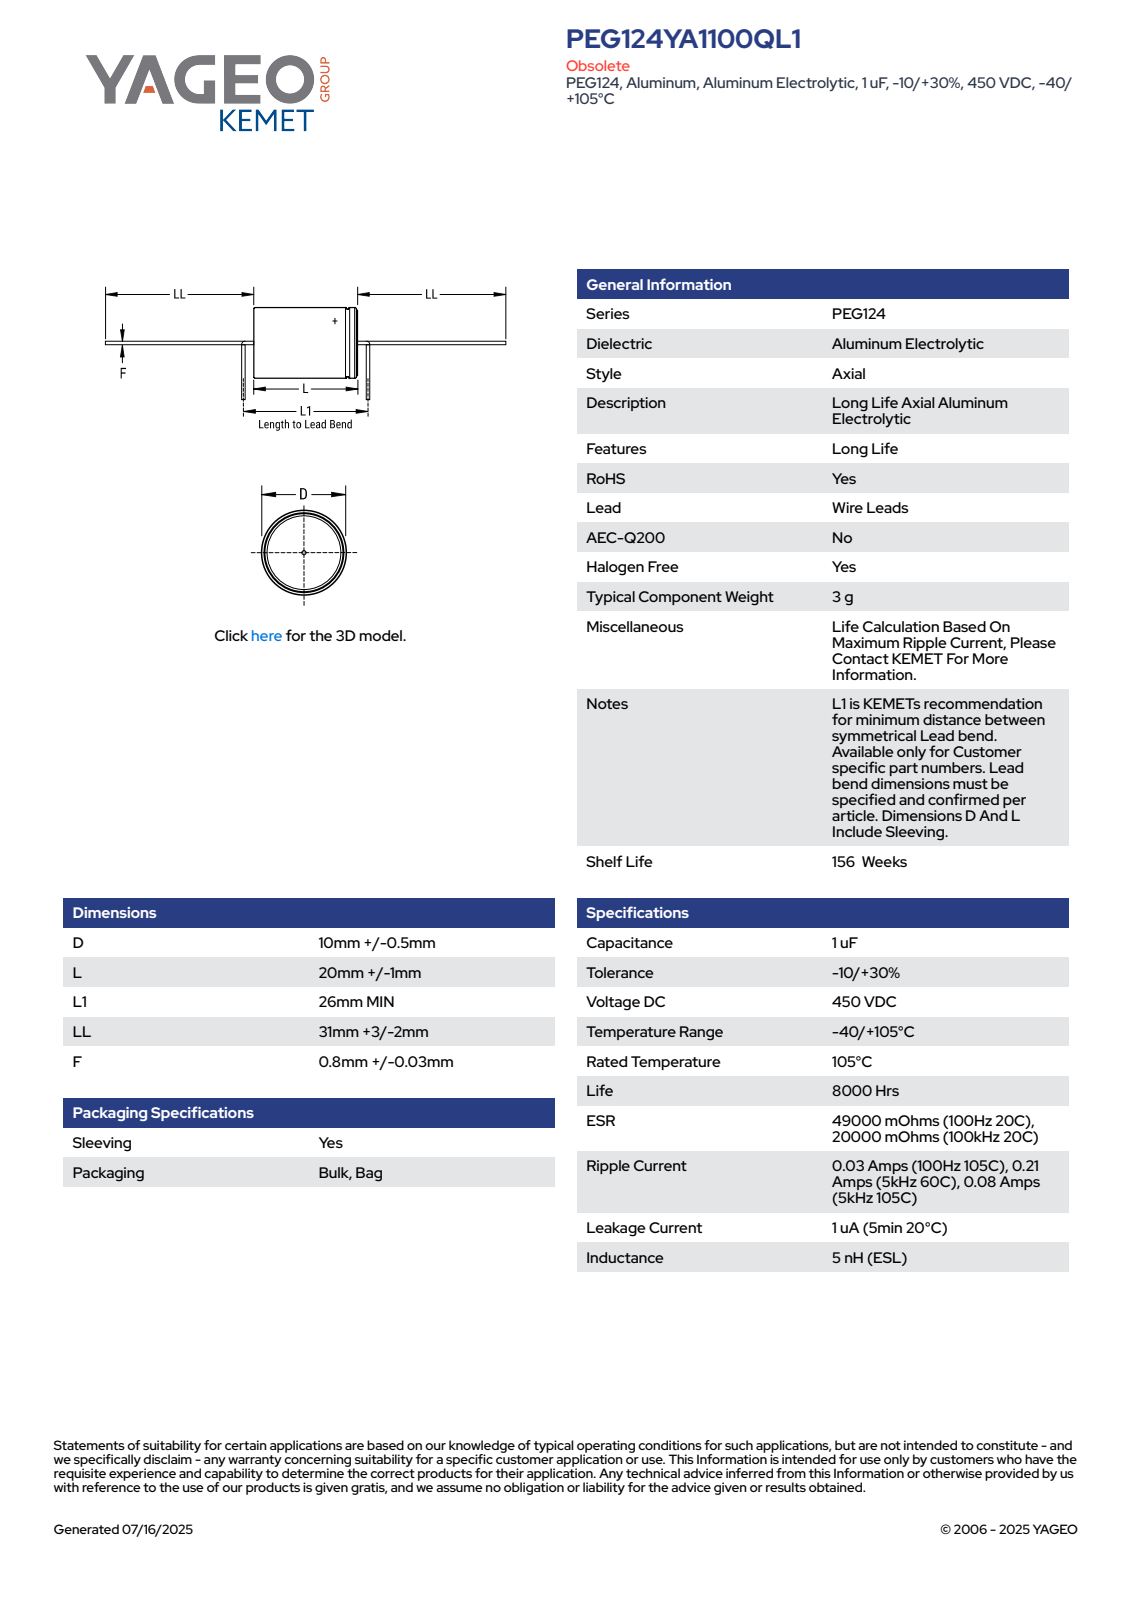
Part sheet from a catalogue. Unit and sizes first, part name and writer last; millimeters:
Units: millimetres
Overall size (bounding box): 97 × 10.5 × 10.5
Round holes (diameter × count): ⌀9.5 ×1
Round bosses / shafts (diameter × count): ⌀10.5 ×1, ⌀10 ×1, ⌀0.83 ×1
Partial cylindrical surfaces — rounded edges, fillets, slot ends (radius × count): R5.24 ×1
Main face-to-face distances: 20, 21, 1, 34, 54, 55, 97, 63, 43, 42
Volume: 1 784 mm³ · Surface area: 1 098 mm²
Bodies: 1 solid, 99 faces (27 planar, 29 cylindrical, 43 other)
Part name (STEP PRODUCT): CAA_PEG124_10X20_D10.5L21LL34F0.83
STEP written by: SolidWorks 2014 (AUTOMOTIVE_DESIGN)
